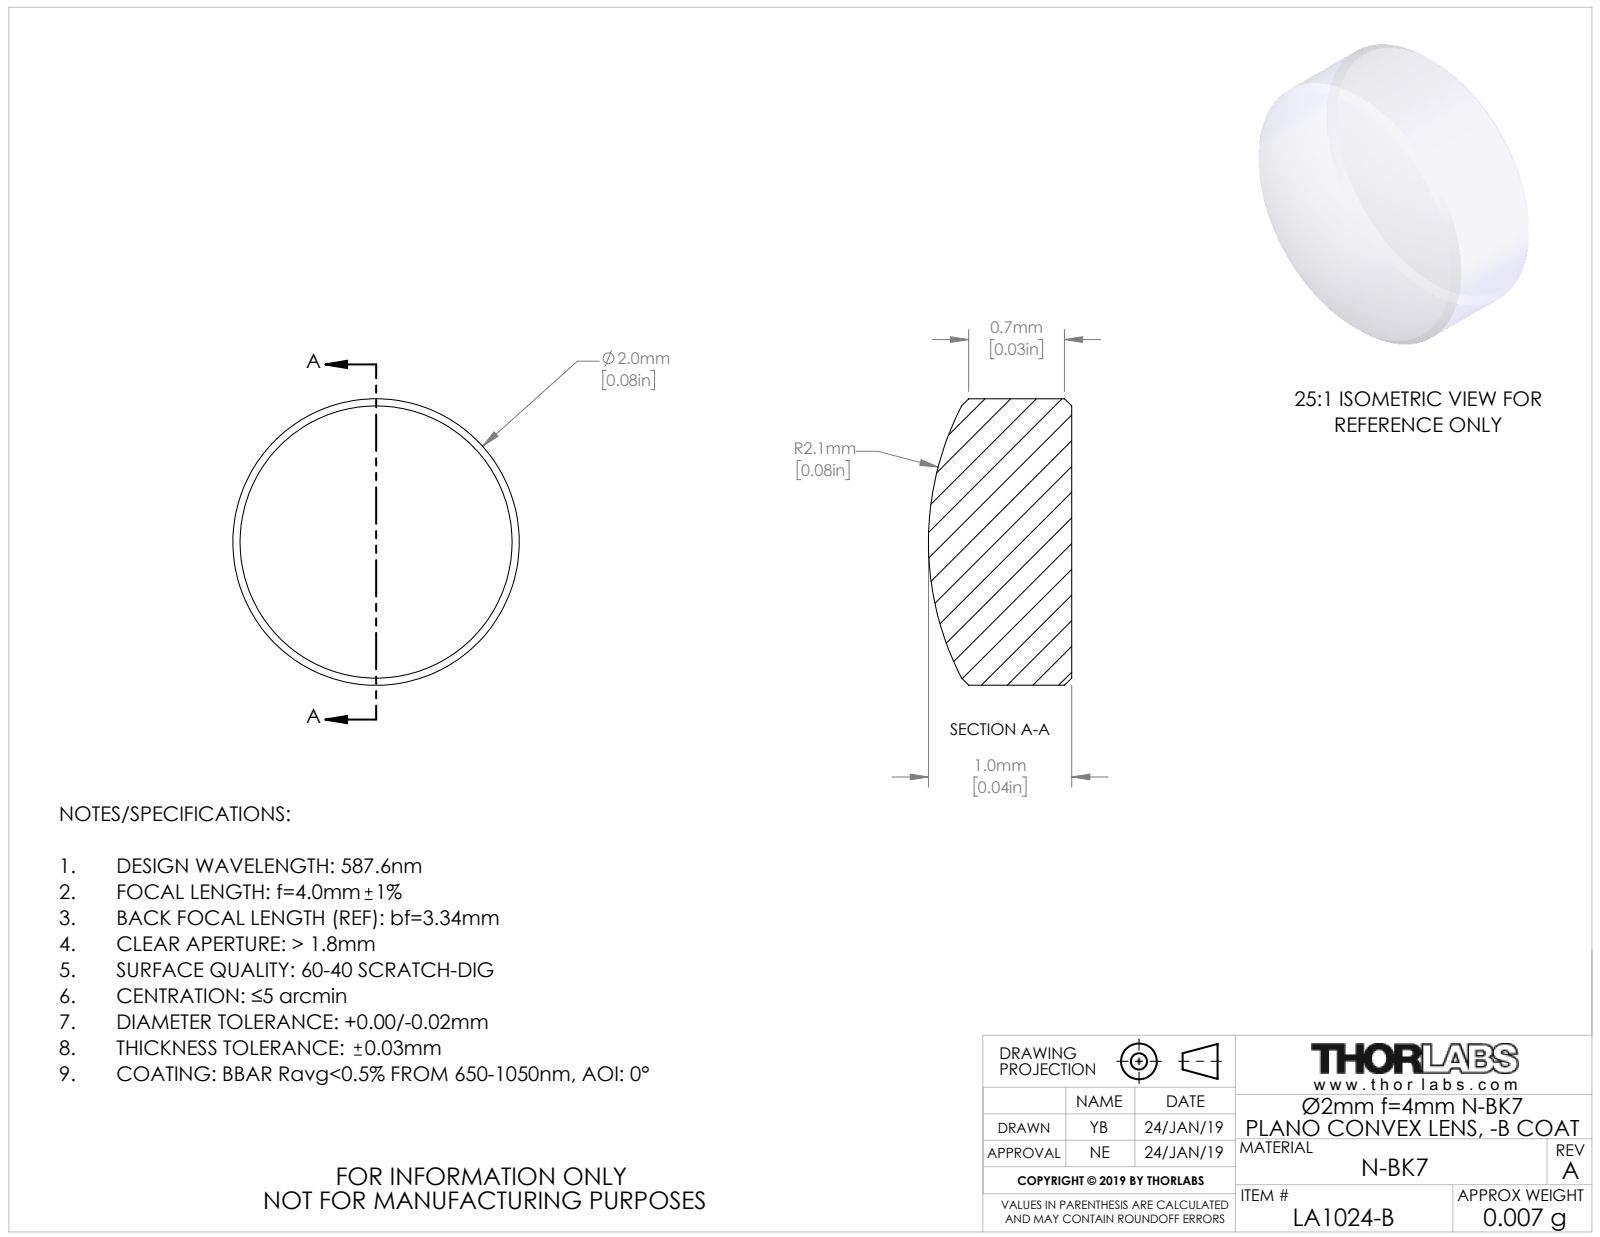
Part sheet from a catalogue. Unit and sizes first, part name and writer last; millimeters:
Units: millimetres
Overall size (bounding box): 2 × 2 × 1
Round bosses / shafts (diameter × count): ⌀2 ×1
Volume: 3 mm³ · Surface area: 11 mm²
Bodies: 1 solid, 9 faces (1 planar, 2 cylindrical, 6 other)
Part name (STEP PRODUCT): TTN162593-E0W
STEP written by: SolidWorks 2018 (CONFIG_CONTROL_DESIGN)
